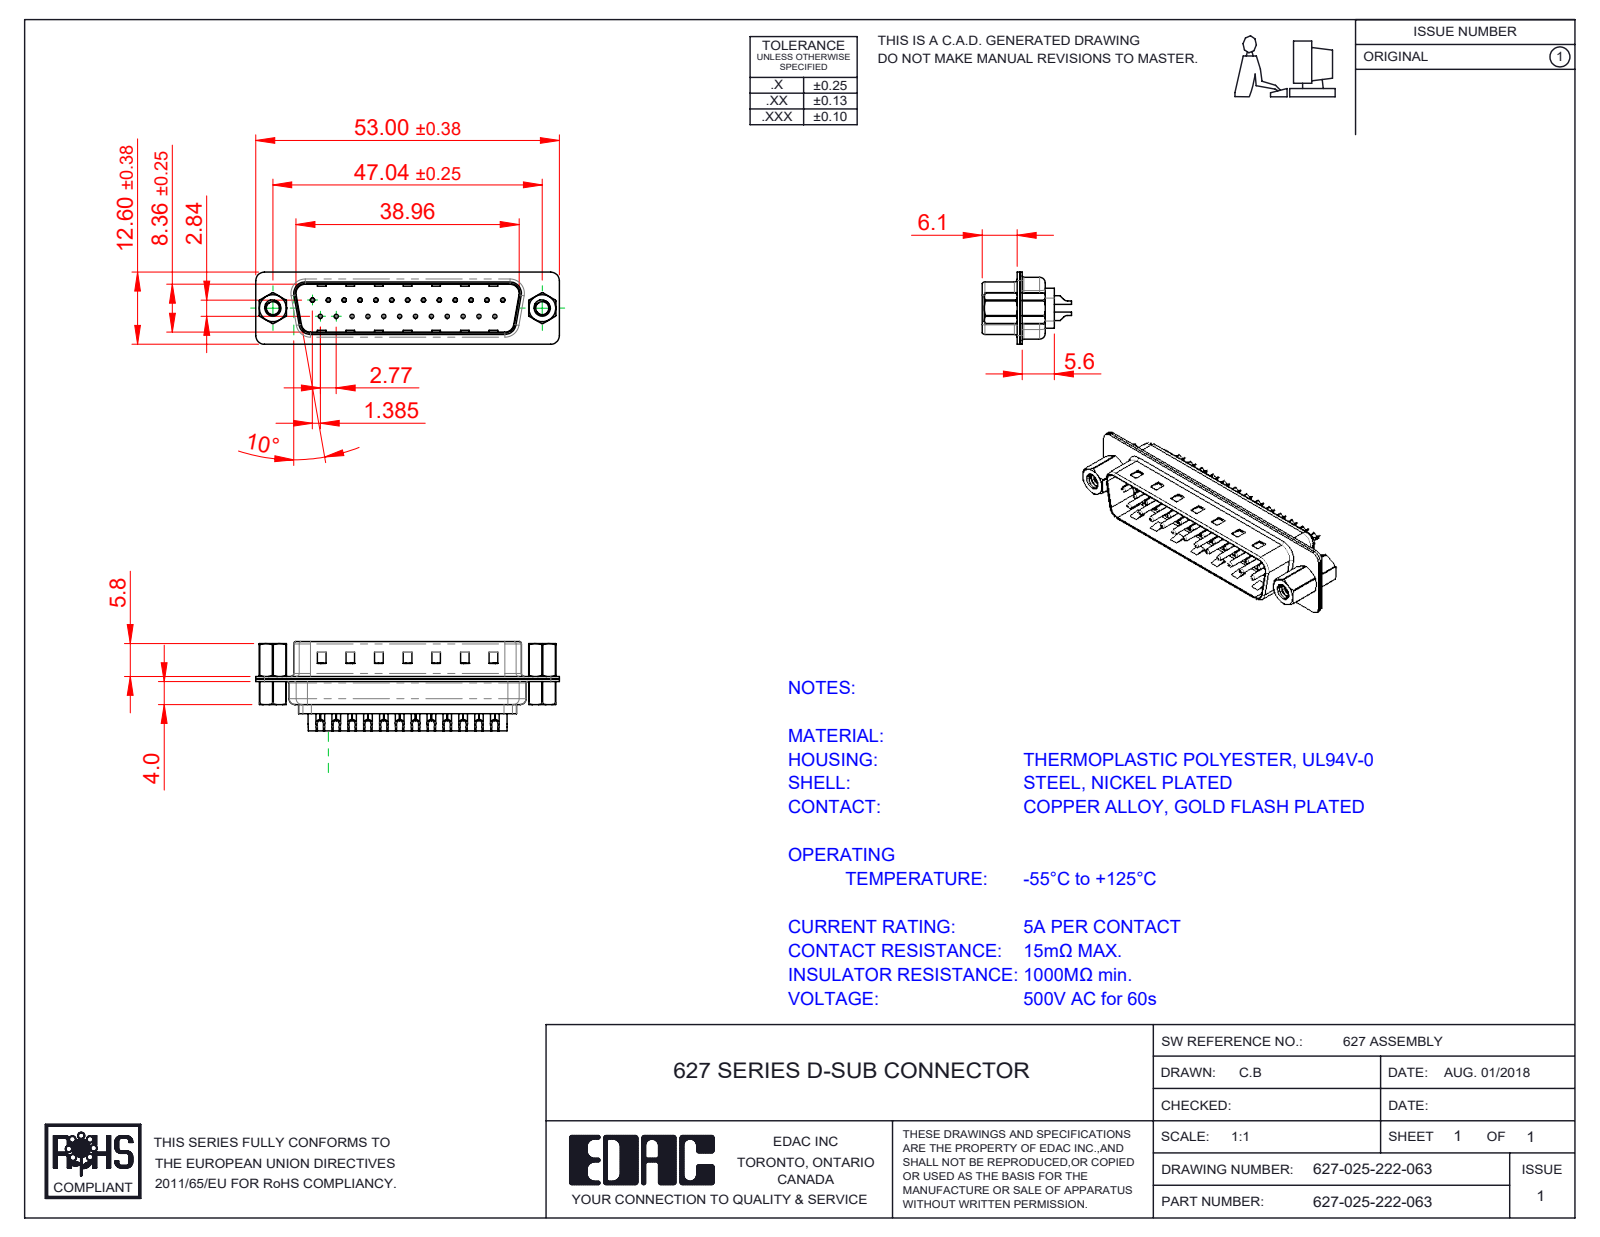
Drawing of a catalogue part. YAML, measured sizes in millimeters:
part_name: "627 Housing_25 LP; 627 Contact Row 2_22L; 627 Shell Front_25 Contacts; 627 4-40 Threaded Rivet (+4 more)"
step_written_by: "SolidWorks 2020 (CONFIG_CONTROL_DESIGN)"
units: millimeters
bodies: {solids: 32, faces: 2098, planar: 543, cylindrical: 932, other: 623}
overall_size: [53, 15.35, 12.6]
volume: 2898
surface_area: 8328
round_holes:
  - {diameter: 0.35, count: 25}
  - {diameter: 1.1, count: 25}
  - {diameter: 1.6, count: 25}
  - {diameter: 2.26, count: 2}
  - {diameter: 2.29, count: 2}
  - {diameter: 4, count: 2}
  - {diameter: 4.8, count: 2}
round_bosses_or_shafts:
  - {diameter: 2, count: 25}
  - {diameter: 1.5, count: 25}
  - {diameter: 0.75, count: 25}
  - {diameter: 5, count: 2}
  - {diameter: 4.9, count: 2}
  - {diameter: 2.79, count: 2}
partial_cylinders:
  - {radius: 1.5, count: 16}
  - {radius: 2, count: 12}
  - {radius: 0.5, count: 8}
  - {radius: 1.6, count: 8}
  - {radius: 1, count: 6}
  - {radius: 0.25, count: 4}
  - {radius: 0.6, count: 4}
  - {radius: 0.65, count: 4}
face_to_face_distances: [0.4, 0.45, 0.82, 9.58, 8.76, 0.9, 1.5, 1.4, 6.5, 6.05]
hole_center_spacings: [3.16, 8.31, 2.77, 5.54, 11.08, 16.62, 5.03, 5.04]
